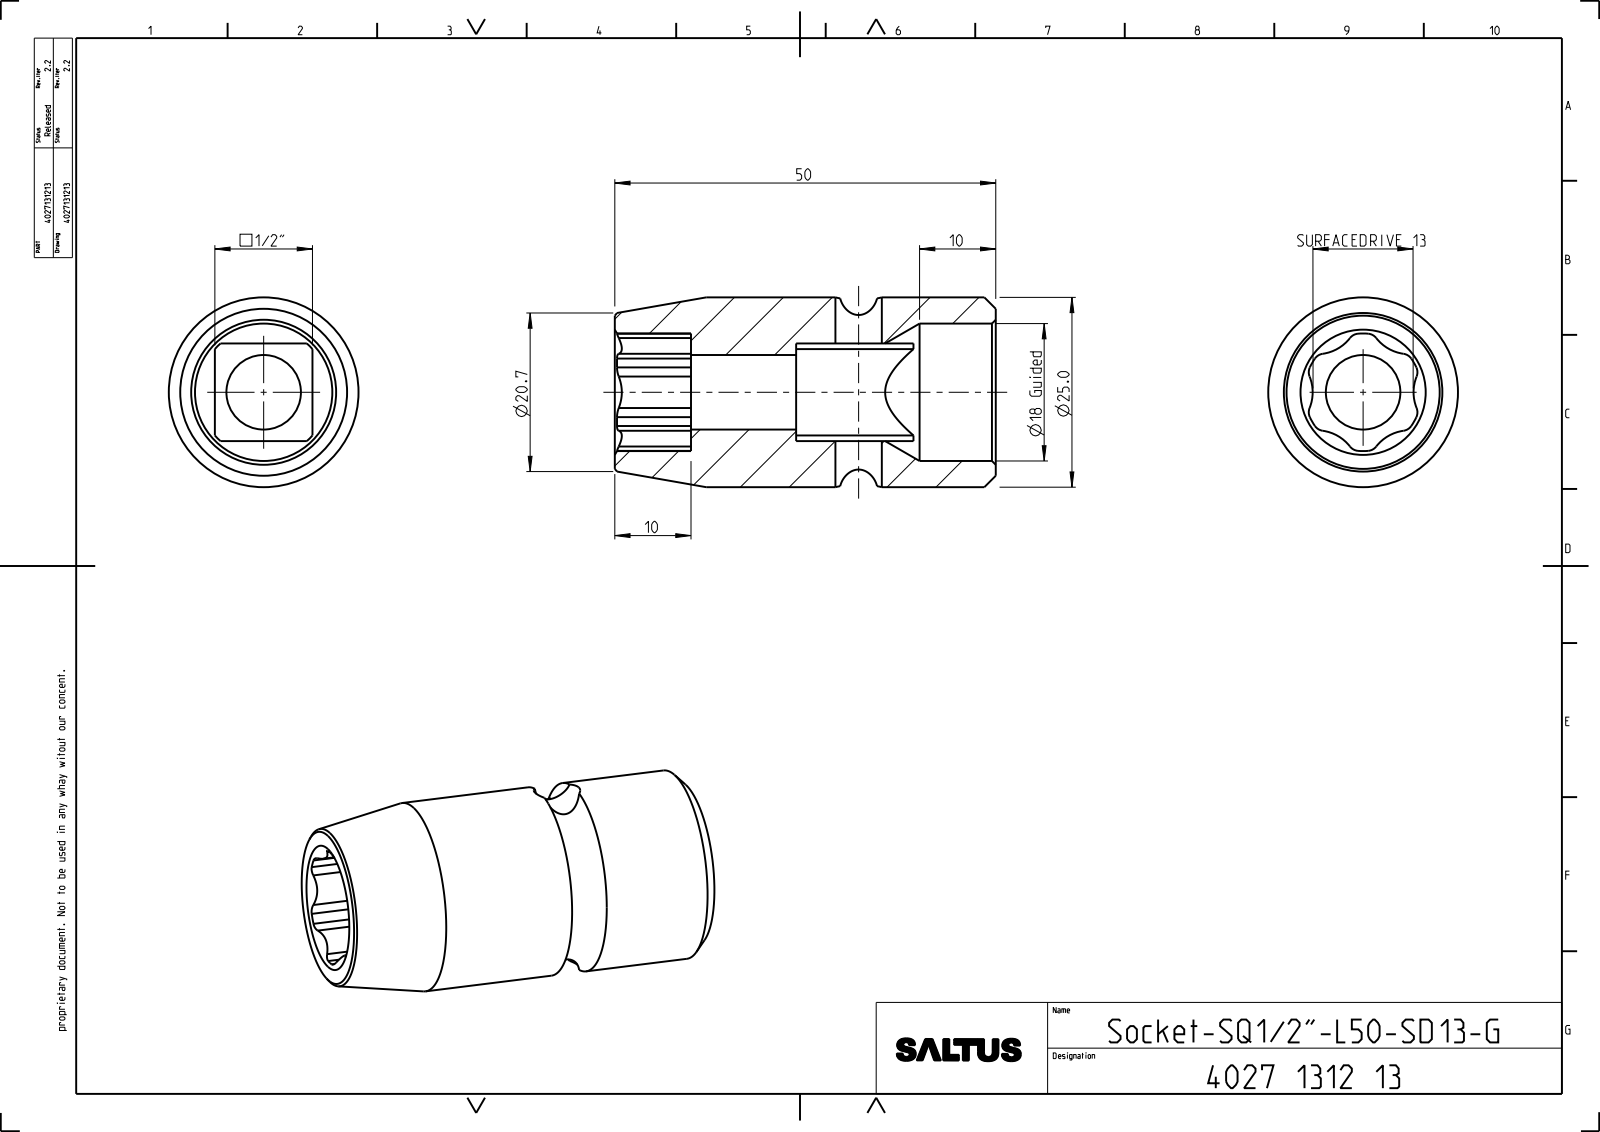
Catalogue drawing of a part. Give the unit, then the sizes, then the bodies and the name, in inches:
Units: inches
Overall size (bounding box): 1.969 × 0.98 × 0.98
Round holes (diameter × count): ⌀0.24 ×1, ⌀0.385 ×1, ⌀0.709 ×1
Round bosses / shafts (diameter × count): ⌀0.98 ×1
Partial cylindrical surfaces — rounded edges, fillets, slot ends (radius × count): R0.059 ×12, R0.217 ×6, R0.304 ×1, R0.337 ×1
Main face-to-face distances: 0.505, 1.969, 1.575, 0.394, 1.031, 0.543, 0.937
Volume: 0.886 in³ · Surface area: 10.49 in²
Bodies: 1 solid, 63 faces (8 planar, 41 cylindrical, 14 other)
Part name (STEP PRODUCT): 4027131213
STEP written by: CREO PARAMETRIC BY PTC INC, 2022414 (CONFIG_CONTROL_DESIGN)
